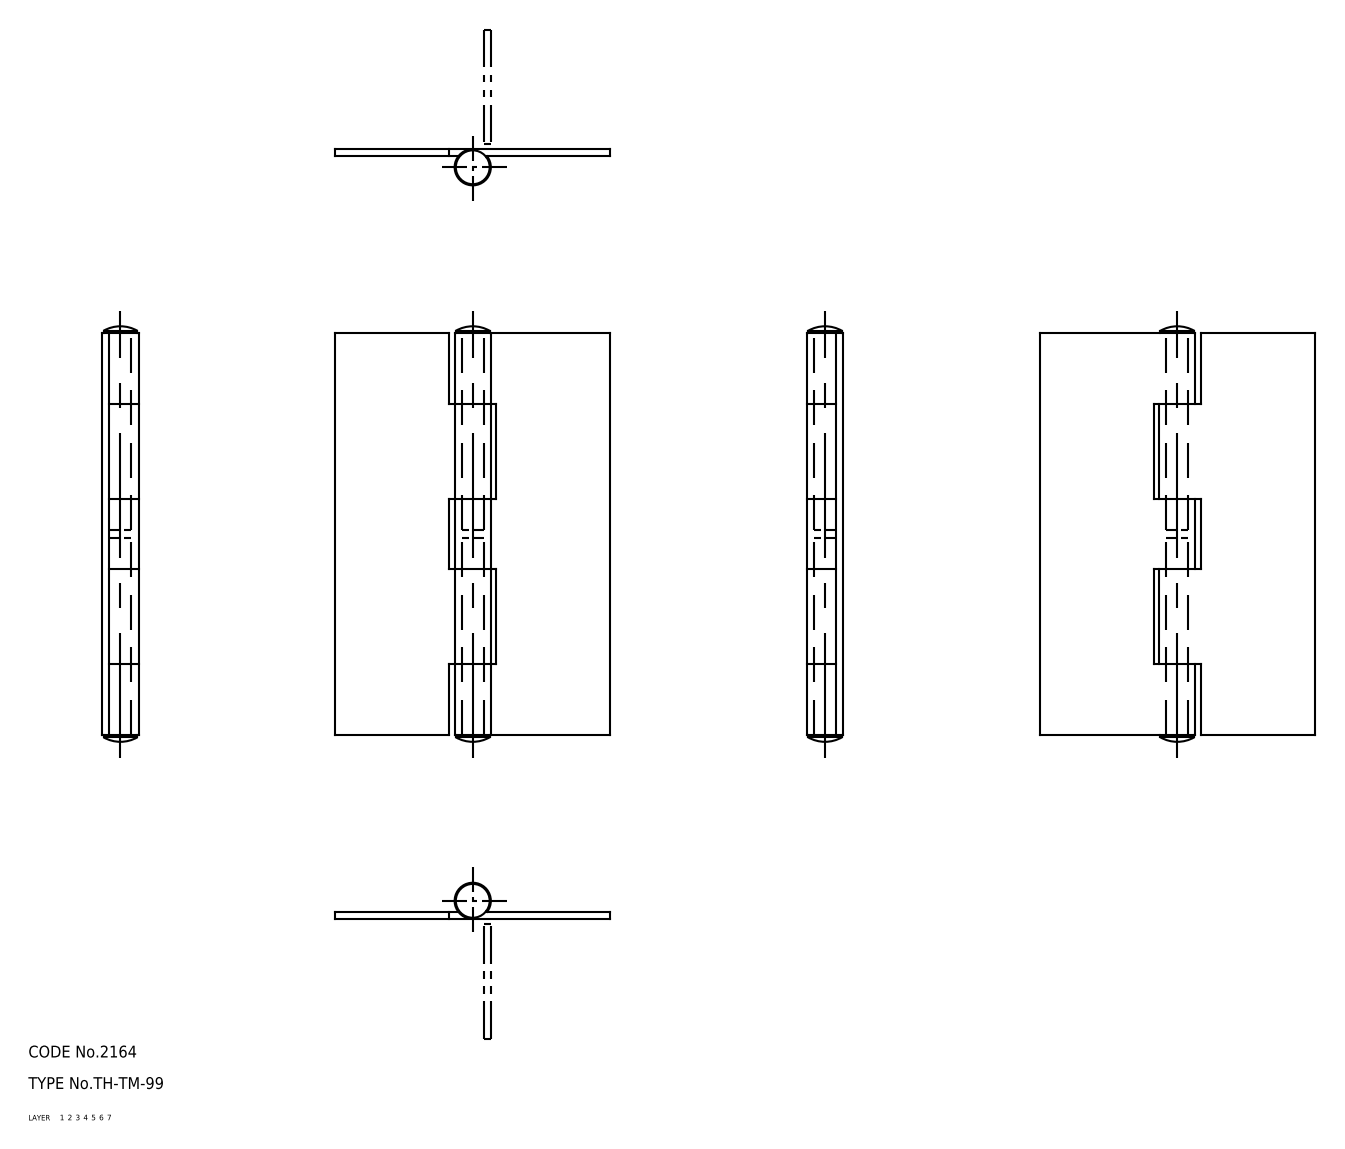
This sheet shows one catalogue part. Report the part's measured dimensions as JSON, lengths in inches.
{"part_name": "67111512; 67111525; 67111538; 67111551", "step_written_by": "CADfix (AUTOMOTIVE_DESIGN)", "units": "inches", "bodies": {"solids": 4, "faces": 52, "planar": 0, "cylindrical": 0, "other": 52}, "overall_size": [4.157, 2.756, 0.362], "volume_in3": 1.098, "surface_area_in2": 31.84}
